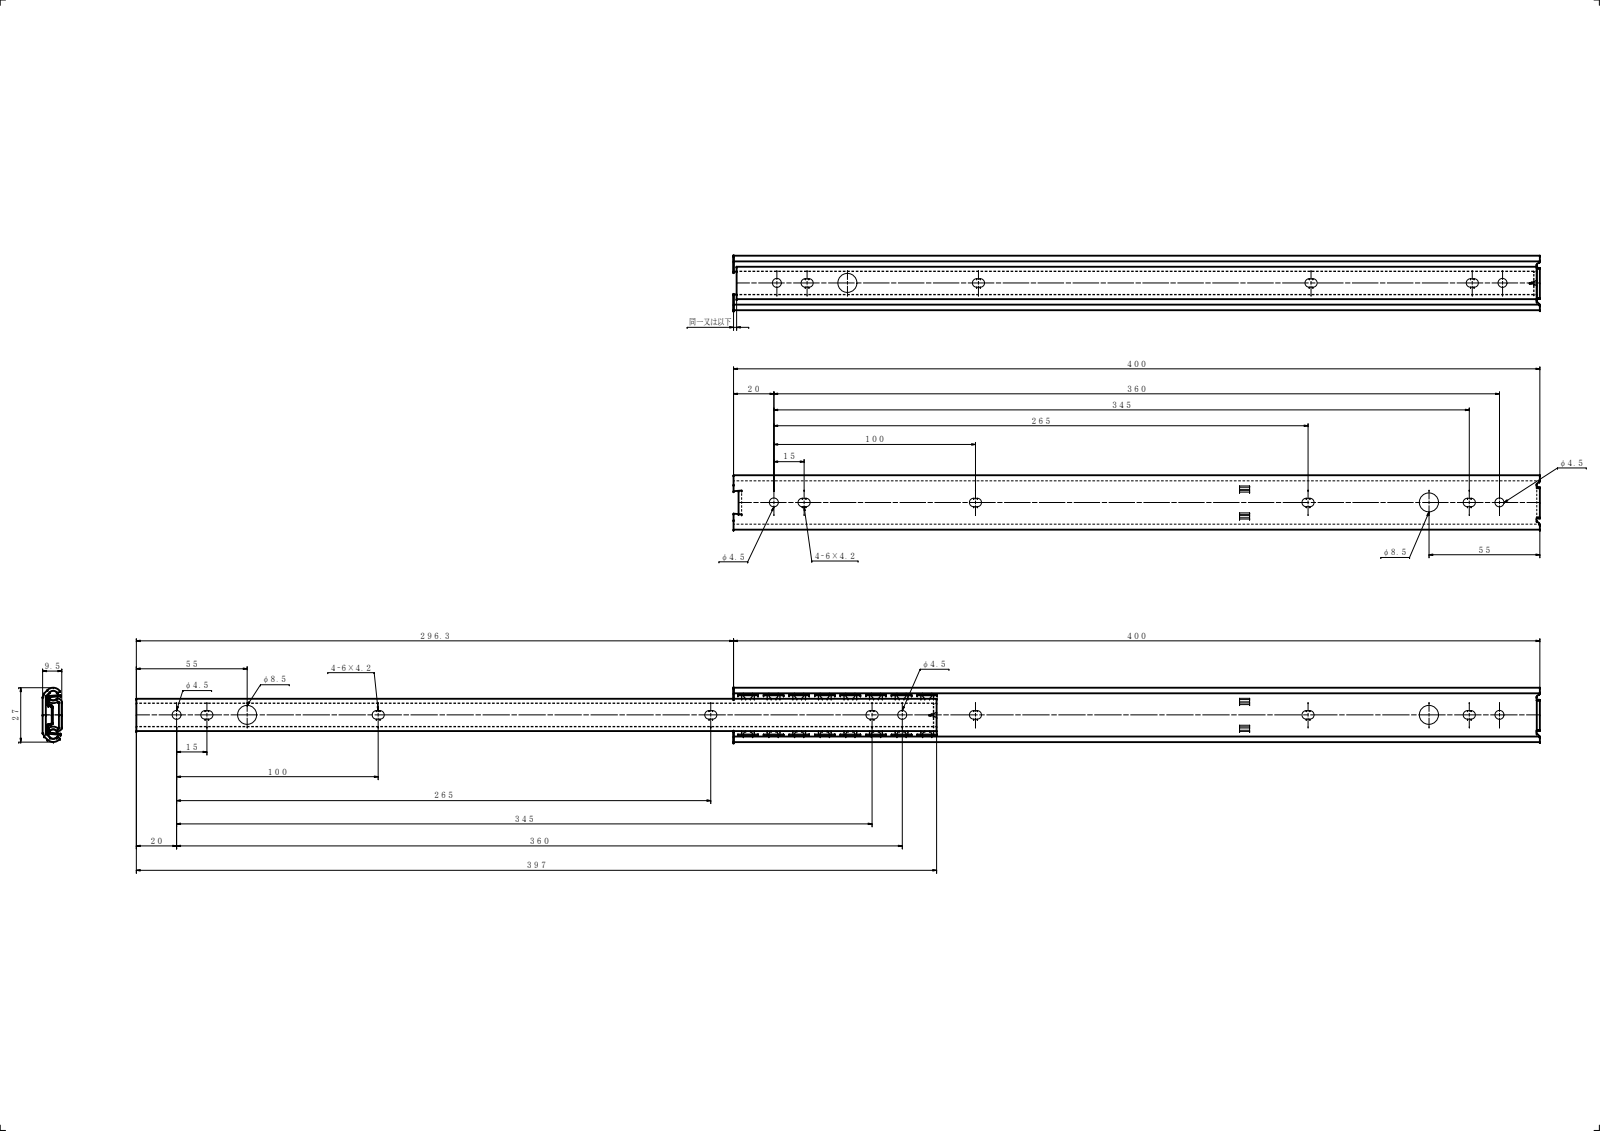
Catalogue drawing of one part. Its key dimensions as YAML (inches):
part_name: "IM-2721-400; 2721-400; OM-2721-400"
step_written_by: "SolidWorks 2019 (CONFIG_CONTROL_DESIGN)"
units: inches
bodies: {solids: 2, faces: 126, planar: 57, cylindrical: 69, other: 0}
overall_size: [27.413, 1.063, 0.374]
volume: 2.285
surface_area: 81.56
round_holes:
  - {diameter: 0.177, count: 4}
  - {diameter: 0.335, count: 2}
partial_cylinders:
  - {radius: 0.083, count: 16}
  - {radius: 0.079, count: 10}
  - {radius: 0.039, count: 8}
  - {radius: 0.011, count: 2}
  - {radius: 0.066, count: 2}
  - {radius: 0.094, count: 2}
  - {radius: 0.118, count: 2}
  - {radius: 0.149, count: 2}
face_to_face_distances: [0.063, 0.055, 0.374, 0.311, 0.319, 0.256, 15.591, 11.783, 11.72, 15.654]
hole_center_spacings: [1.378, 10.287, 11.665, 12.795, 14.173, 24.461, 2.508, 23.083]
